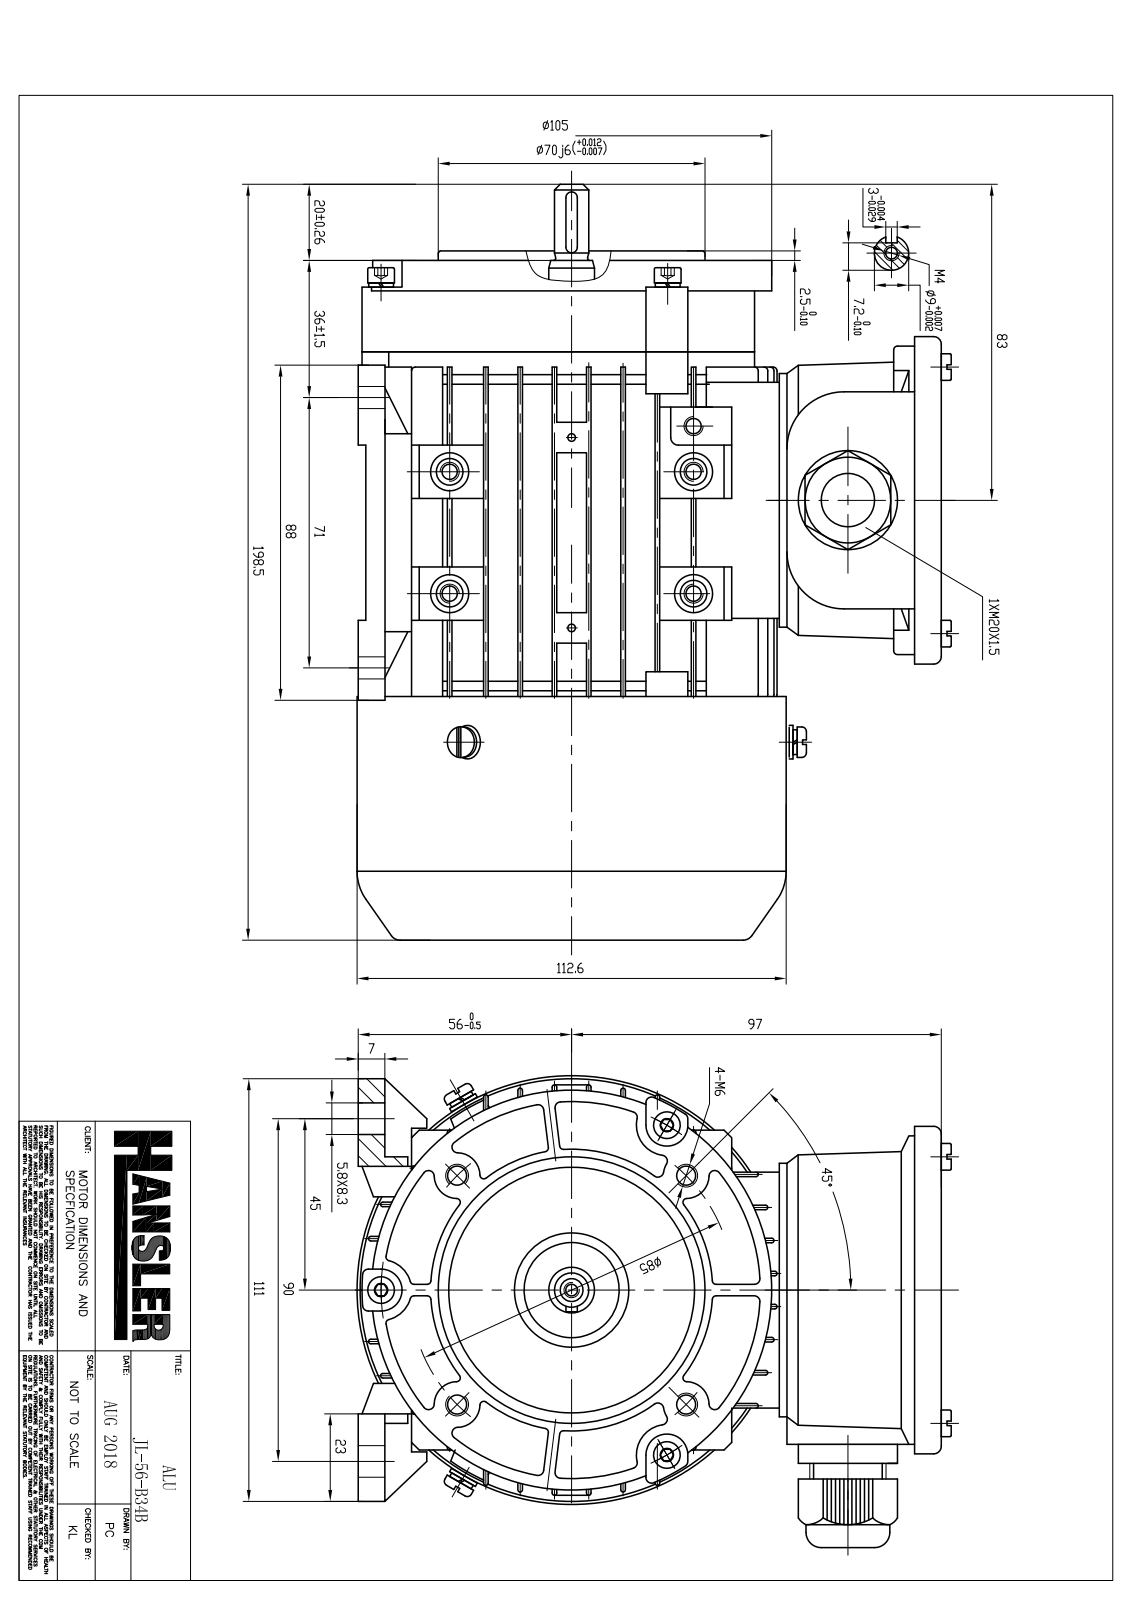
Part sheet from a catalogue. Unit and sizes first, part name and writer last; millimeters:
Units: millimetres
Overall size (bounding box): 198.42 × 154.7 × 119.88
Round holes (diameter × count): ⌀3 ×18, ⌀4 ×13, ⌀4.7 ×10, ⌀4.25 ×9, ⌀6 ×8, ⌀10 ×8, ⌀4.13 ×4, ⌀5 ×4, ⌀5.25 ×4, ⌀7.5 ×4, ⌀12 ×4, ⌀2 ×3
Round bosses / shafts (diameter × count): ⌀7 ×11, ⌀3.55 ×10, ⌀6.45 ×9, ⌀4 ×9, ⌀9.5 ×4, ⌀8.5 ×4, ⌀7.85 ×4, ⌀5 ×4
Partial cylindrical surfaces — rounded edges, fillets, slot ends (radius × count): R0.5 ×260, R1.5 ×58, R1 ×45, R2 ×39, R3 ×36, R5 ×16, R6 ×16, R2.9 ×8
Main face-to-face distances: 2, 8.68, 17.36, 6, 26.04, 1.2, 34.72, 4, 9.88, 7.48
Hole centre spacings: 31.85, 44, 50, 57.95, 58.46, 86.6, 32, 19.5
Volume: 509 405 mm³ · Surface area: 394 789 mm²
Bodies: 48 solids, 3574 faces (1928 planar, 1296 cylindrical, 350 other)
Part name (STEP PRODUCT): JL-56-B34B
STEP written by: SIEMENS PLM Software NX 12.0 (AP203_CONFIGURATION_CONTROLLED_3D_DESIGN_OF_MECHANICAL_PARTS_AND_ASSEMBLIES_MIM_LF)
